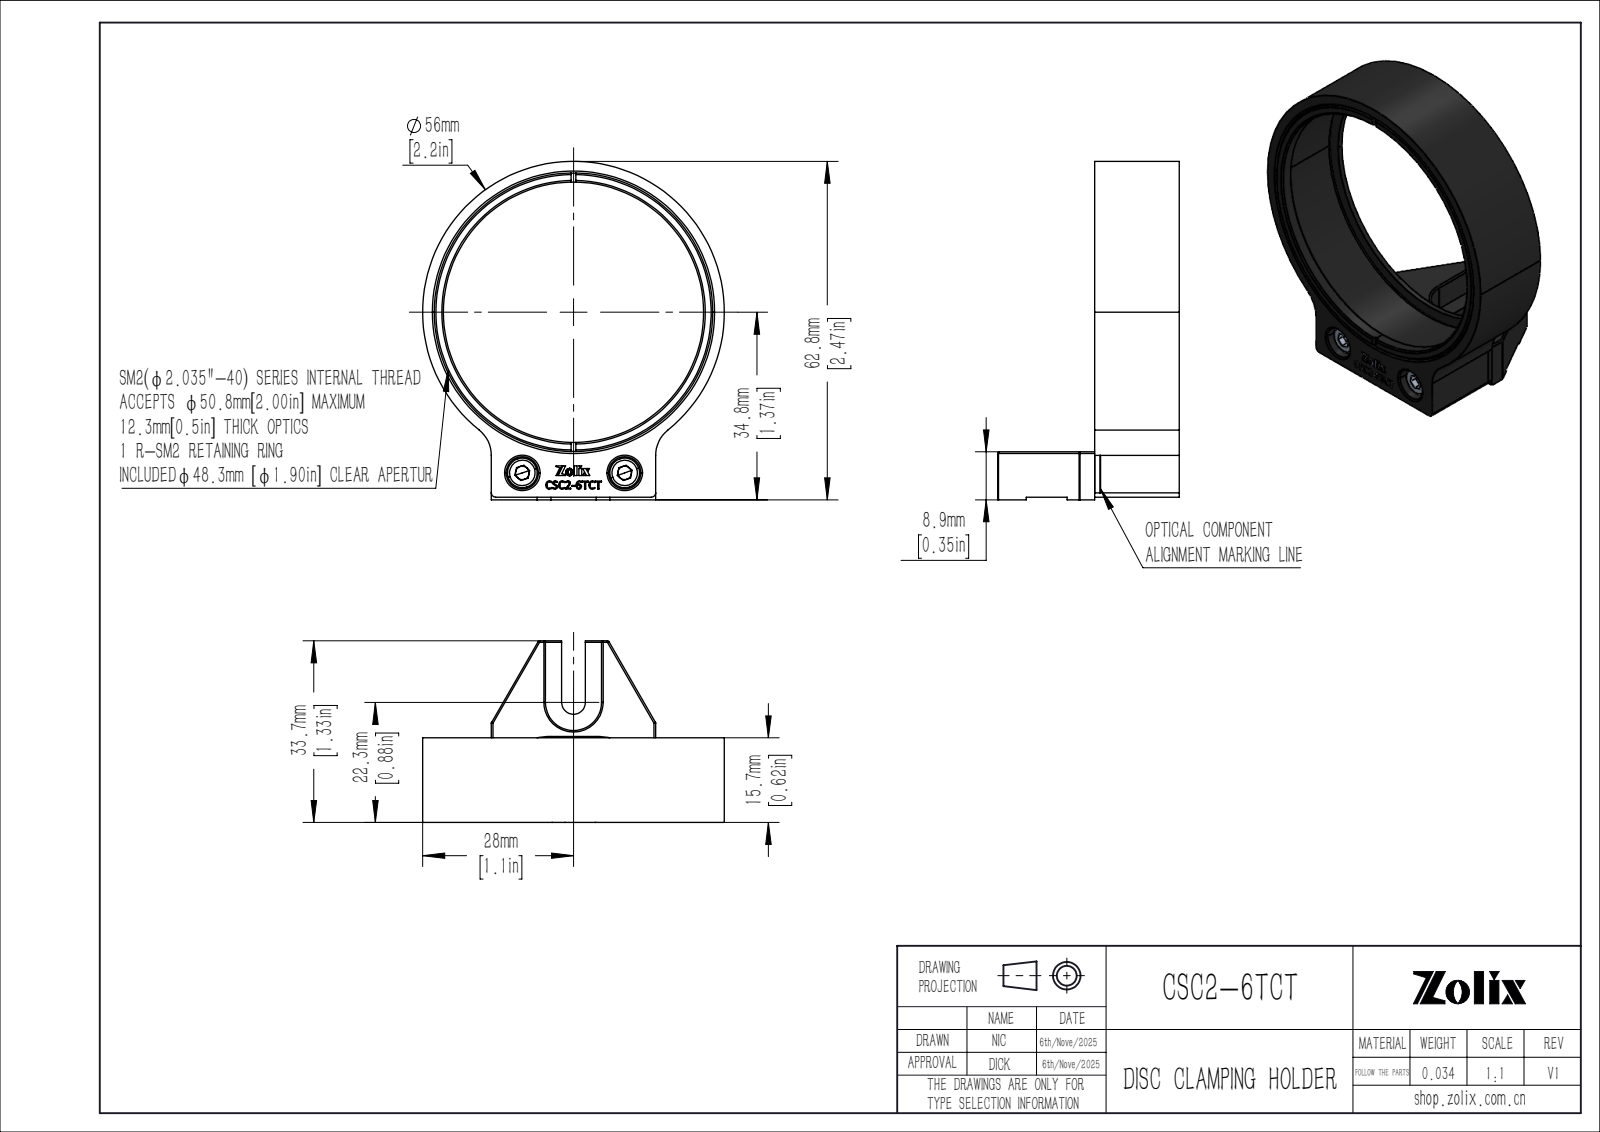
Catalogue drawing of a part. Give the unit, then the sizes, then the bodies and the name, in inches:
Units: inches
Overall size (bounding box): 2.472 × 2.205 × 1.327
Round holes (diameter × count): ⌀0.063 ×2, ⌀0.098 ×2, ⌀0.134 ×2, ⌀0.236 ×2, ⌀1.902 ×1, ⌀2.031 ×1, ⌀2.071 ×1
Round bosses / shafts (diameter × count): ⌀0.217 ×2, ⌀0.118 ×2, ⌀2.035 ×1
Partial cylindrical surfaces — rounded edges, fillets, slot ends (radius × count): R0.012 ×14, R0.031 ×4, R0.236 ×2, R0.516 ×2, R0.087 ×1, R0.205 ×1, R1.102 ×1
Main face-to-face distances: 0.618, 0.039, 0.579, 0.331, 0.02, 0.35, 0.098, 0.52, 0.48, 1.201
Hole centre spacings: 0.274, 0.502, 1.231, 1.277, 0.236, 0.748
Volume: 0.771 in³ · Surface area: 17.34 in²
Bodies: 5 solids, 484 faces (289 planar, 68 cylindrical, 127 other)
Part name (STEP PRODUCT): CSC2-6TCT
STEP written by: SolidWorks 2020 (CONFIG_CONTROL_DESIGN)
